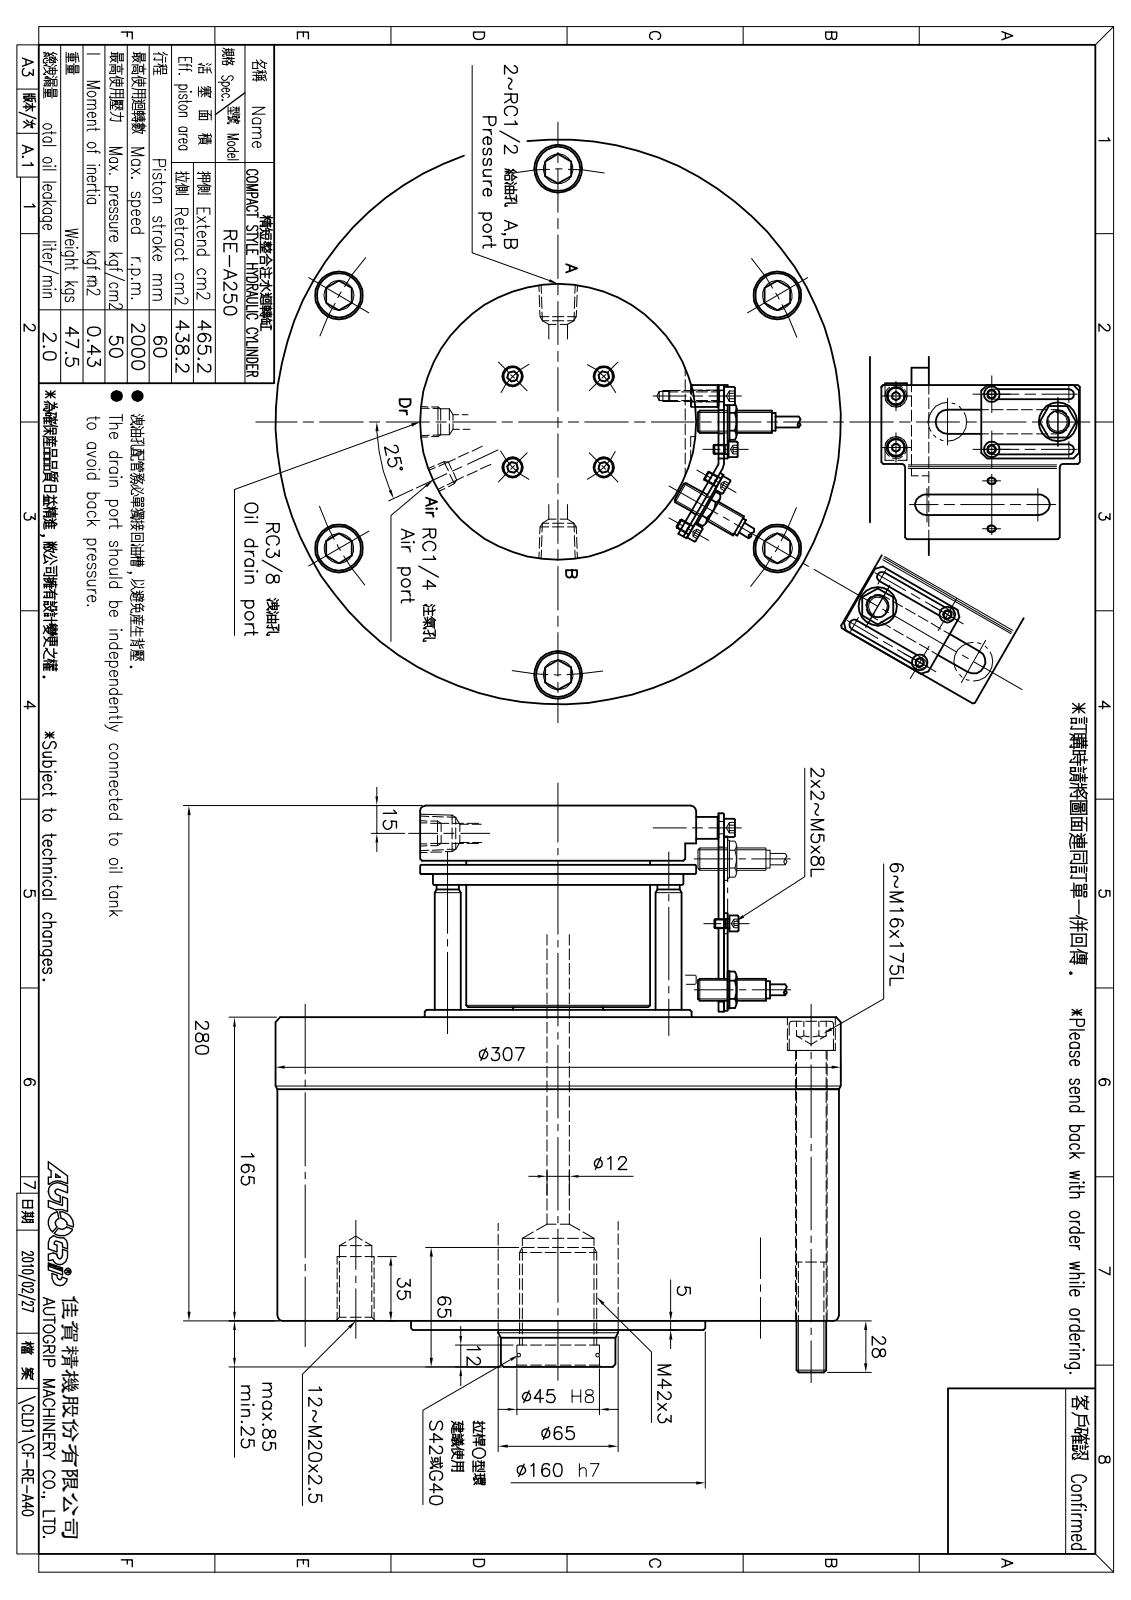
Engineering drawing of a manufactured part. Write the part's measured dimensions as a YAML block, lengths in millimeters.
part_name: "圓頭內六角螺栓_M5x8; CF-RE-250缸體; CF-RE-A250; CF-RE-18-03000 (+5 more)"
step_written_by: "SolidWorks 2016 (CONFIG_CONTROL_DESIGN)"
units: millimeters
bodies: {solids: 22, faces: 644, planar: 279, cylindrical: 209, other: 156}
overall_size: [308, 307, 307]
volume: 10560000
surface_area: 977224
round_holes:
  - {diameter: 17.5, count: 13}
  - {diameter: 17, count: 6}
  - {diameter: 26, count: 6}
  - {diameter: 4.1, count: 4}
  - {diameter: 12, count: 4}
  - {diameter: 5, count: 2}
  - {diameter: 6, count: 2}
  - {diameter: 6.6, count: 2}
  - {diameter: 10.7, count: 1}
  - {diameter: 14.3, count: 1}
  - {diameter: 39, count: 1}
  - {diameter: 42, count: 1}
round_bosses_or_shafts:
  - {diameter: 24, count: 6}
  - {diameter: 16, count: 6}
  - {diameter: 8.5, count: 4}
  - {diameter: 5, count: 4}
  - {diameter: 10, count: 2}
  - {diameter: 307, count: 1}
  - {diameter: 305, count: 1}
  - {diameter: 160, count: 1}
partial_cylinders:
  - {radius: 2.75, count: 8}
  - {radius: 6.5, count: 4}
  - {radius: 1.5, count: 2}
  - {radius: 0.74, count: 1}
  - {radius: 3.74, count: 1}
face_to_face_distances: [59, 30, 115, 39, 85, 114, 29, 9, 135, 1]
hole_center_spacings: [110, 56.94, 98.06, 137.5, 152.24, 155.56, 190.52, 197.07]
